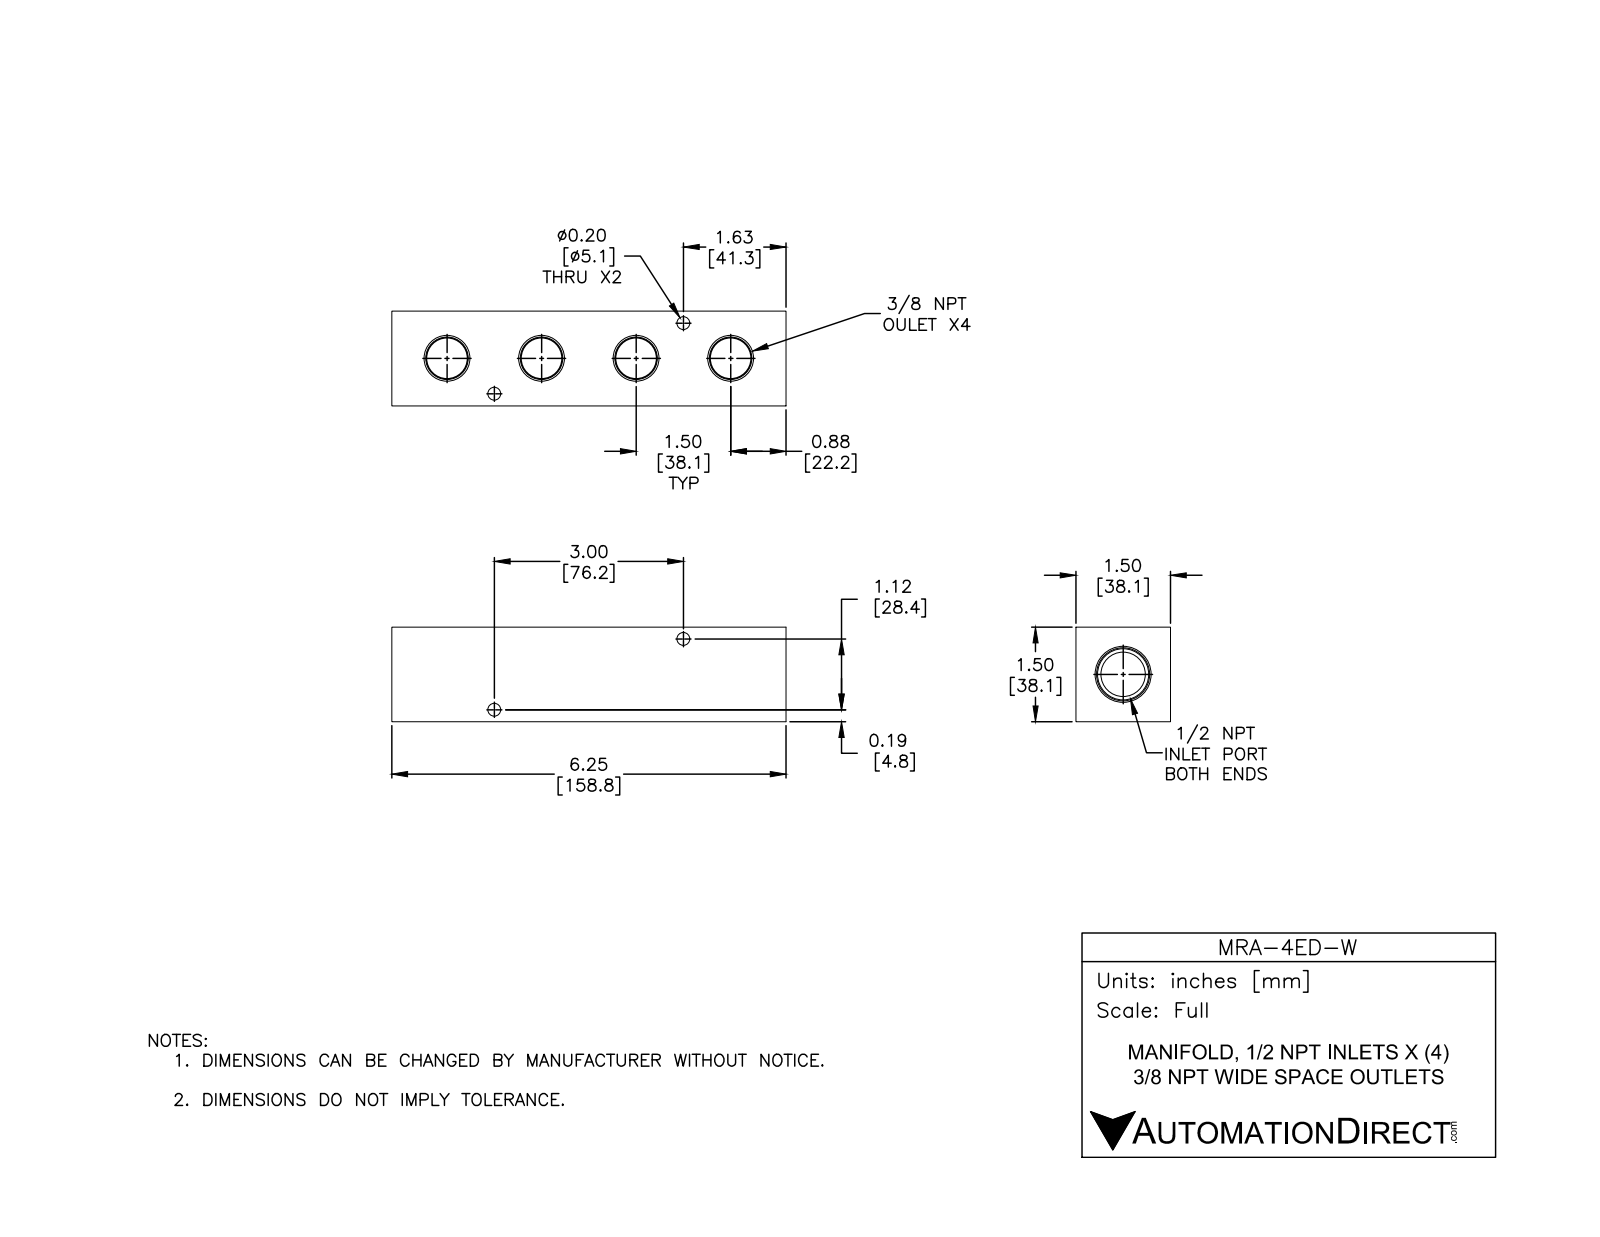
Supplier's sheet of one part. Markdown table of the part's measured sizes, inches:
| quantity | value |
| --- | --- |
| part name | MRA-4ED-W |
| STEP written by | SolidWorks 2015 (CONFIG_CONTROL_DESIGN) |
| units | inches |
| bodies | 1 solid, 66 faces (16 planar, 26 cylindrical, 24 other) |
| overall size | 6.25 × 1.5 × 1.5 |
| volume | 10.71 in³ |
| surface area | 59.85 in² |
| round holes (diameter × count) | 0.2 × 4, 0.562 × 4, 0.703 × 1 |
| main face-to-face distances | 1.5, 6.25, 1.09, 0.41, 0.53, 5.72, 5.19 |
| hole center spacings | 1.5, 0.932, 0.94, 3, 3.202, 2.314, 2.324, 3.787 |
